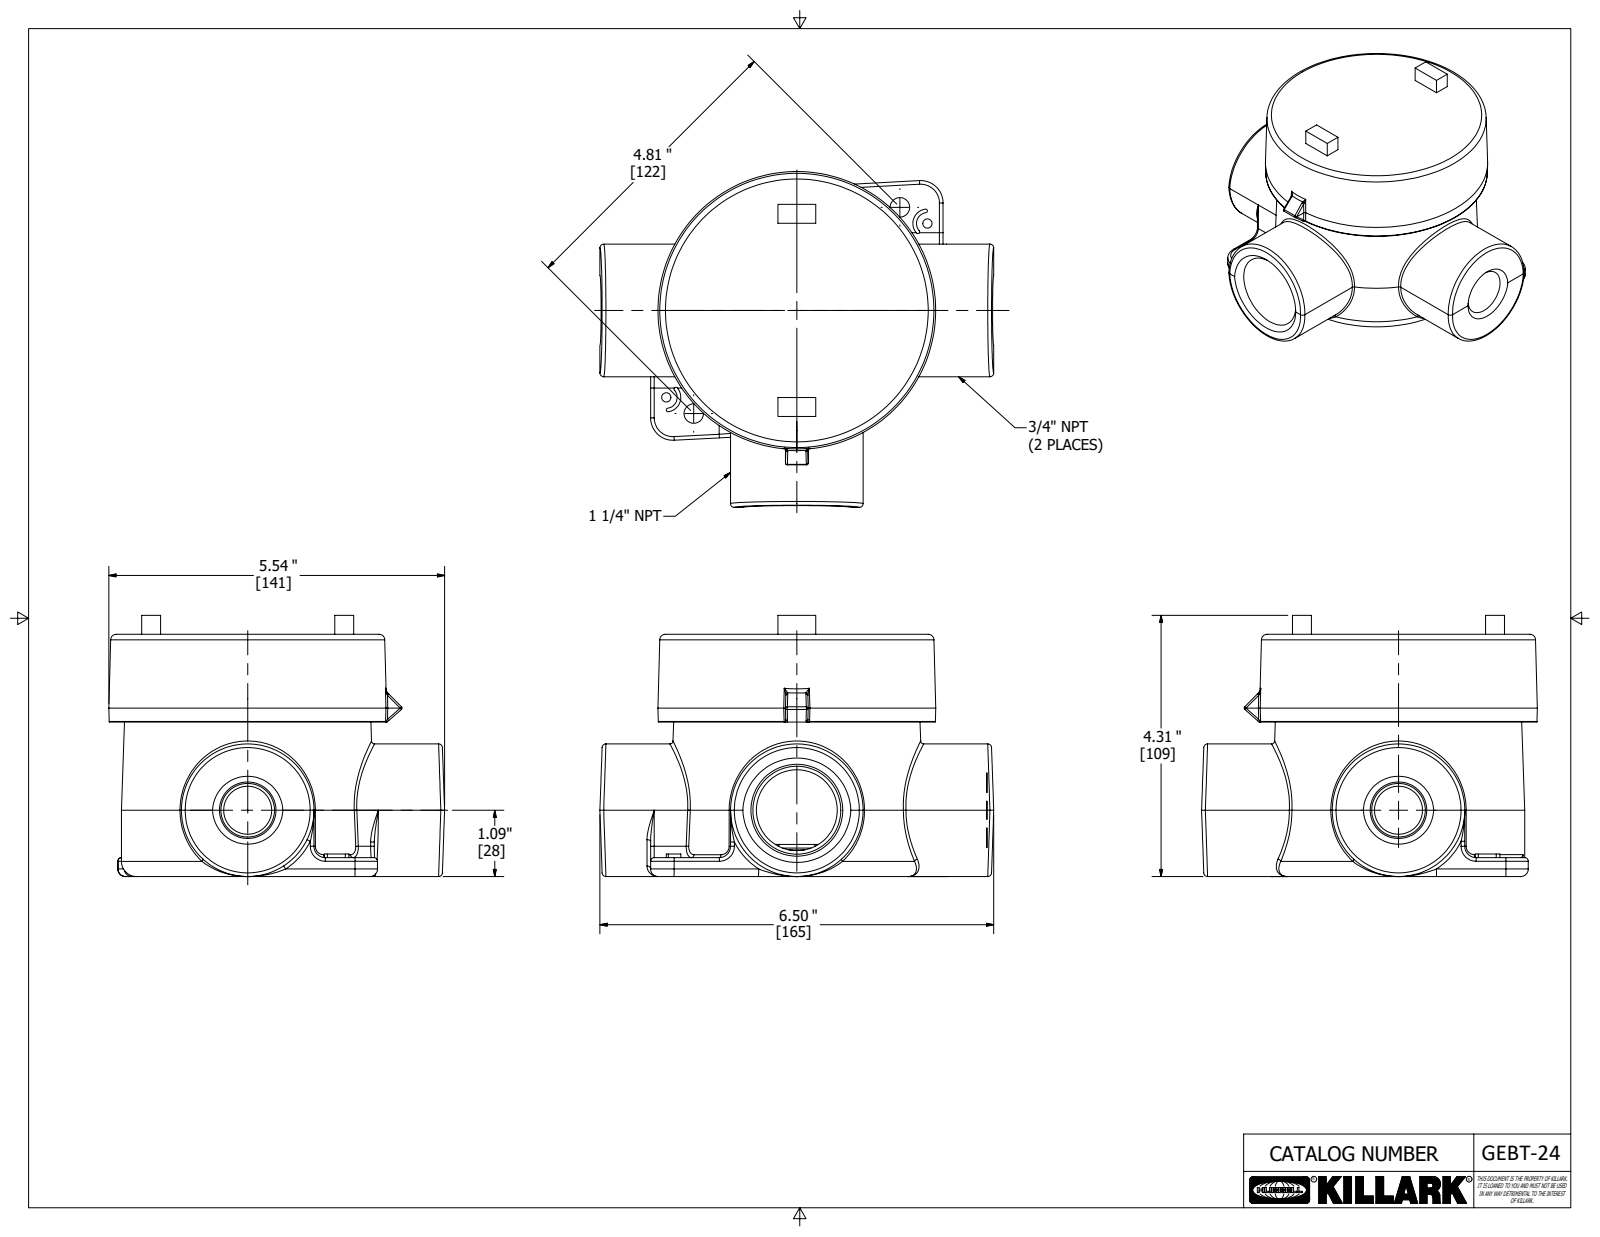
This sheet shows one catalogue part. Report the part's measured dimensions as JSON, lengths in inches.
{"part_name": "GEBT-24; 21414; 21147-override", "step_written_by": "Autodesk Inventor 2020 (AUTOMOTIVE_DESIGN)", "units": "inches", "bodies": {"solids": 2, "faces": 861, "planar": 444, "cylindrical": 95, "other": 322}, "overall_size": [6.5, 5.542, 4.31], "volume_in3": 39.62, "surface_area_in2": 213.5, "round_holes": [[0.153, 2], [0.321, 2], [1.558, 2], [0.792, 1], [1.334, 1], [3.823, 1], [4.045, 1]], "round_bosses_or_shafts": [[2.188, 2]], "partial_cylinders_radius": [[0.06, 34], [0.03, 14], [0.125, 4], [0.031, 3], [0.187, 3], [0.18, 2], [0.24, 2], [0.37, 2]], "face_to_face_distances": [3.998, 3.56, 0.438, 2.549, 1.011, 1.449, 3.5, 0.38, 2.169, 3.18], "hole_center_spacings": [0.527, 4.97, 2.406, 2.406, 2.589, 2.589, 4.812, 5.178]}
